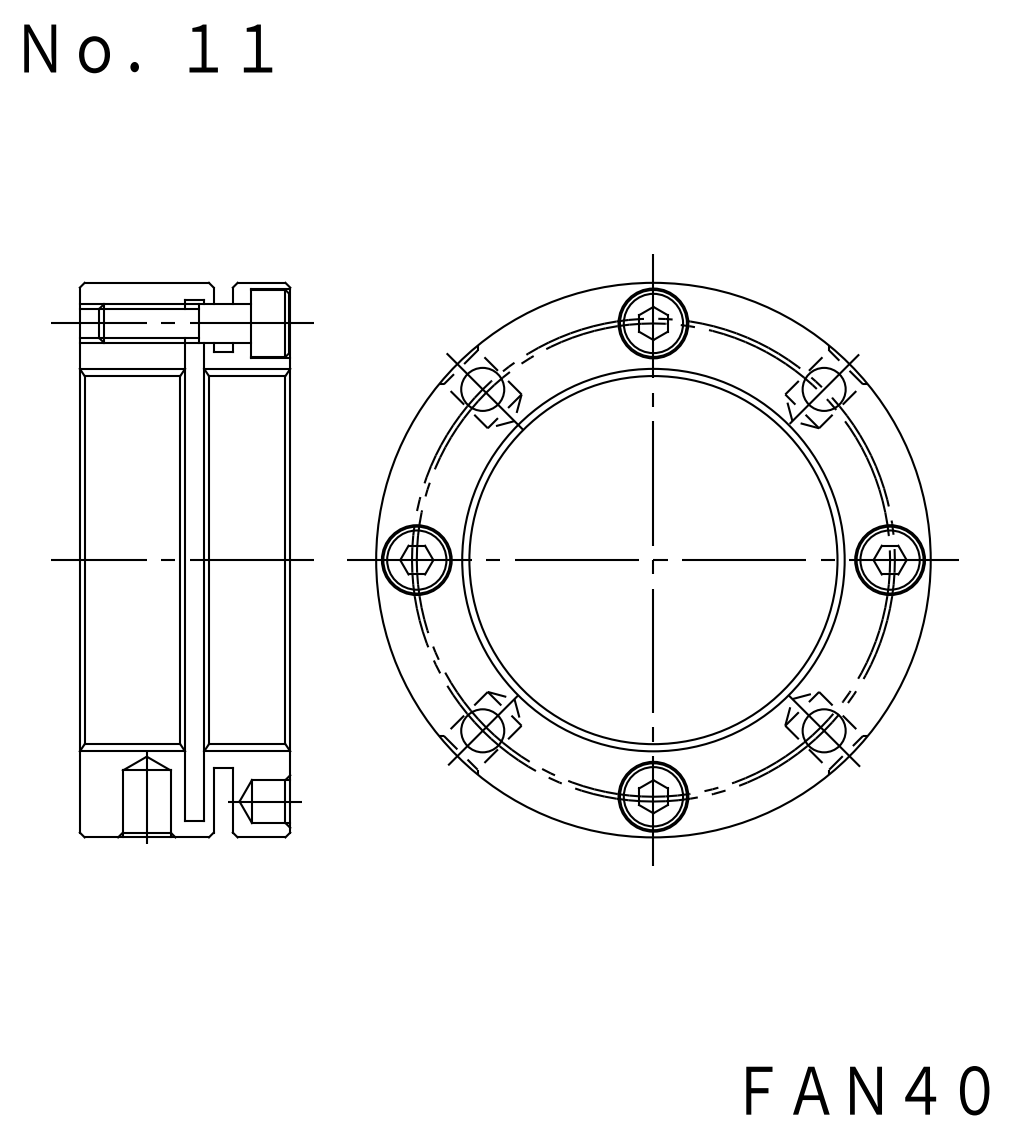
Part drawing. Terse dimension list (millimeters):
name: FKD FAN40; M4X16_default
written by: SolidWorks 2012 (CONFIG_CONTROL_DESIGN)
unit: mm
bodies: 5 solids, 142 faces (50 planar, 76 cylindrical, 16 other)
size: 58 × 58 × 22
volume: 25 527 mm³; area: 16 682 mm²
holes: 4× ⌀3.24, 4× ⌀4.3, 4× ⌀4.5, 4× ⌀5, 4× ⌀7.3, 1× ⌀40, 1× ⌀54
bosses: 4× ⌀7, 4× ⌀4, 1× ⌀58, 1× ⌀44
face distances: 2, 3, 11, 22, 16, 14, 8, 6, 5, 13
hole spacings: 19.05, 45.96, 24.5, 25.24, 34.65, 35.7, 49, 50.49
